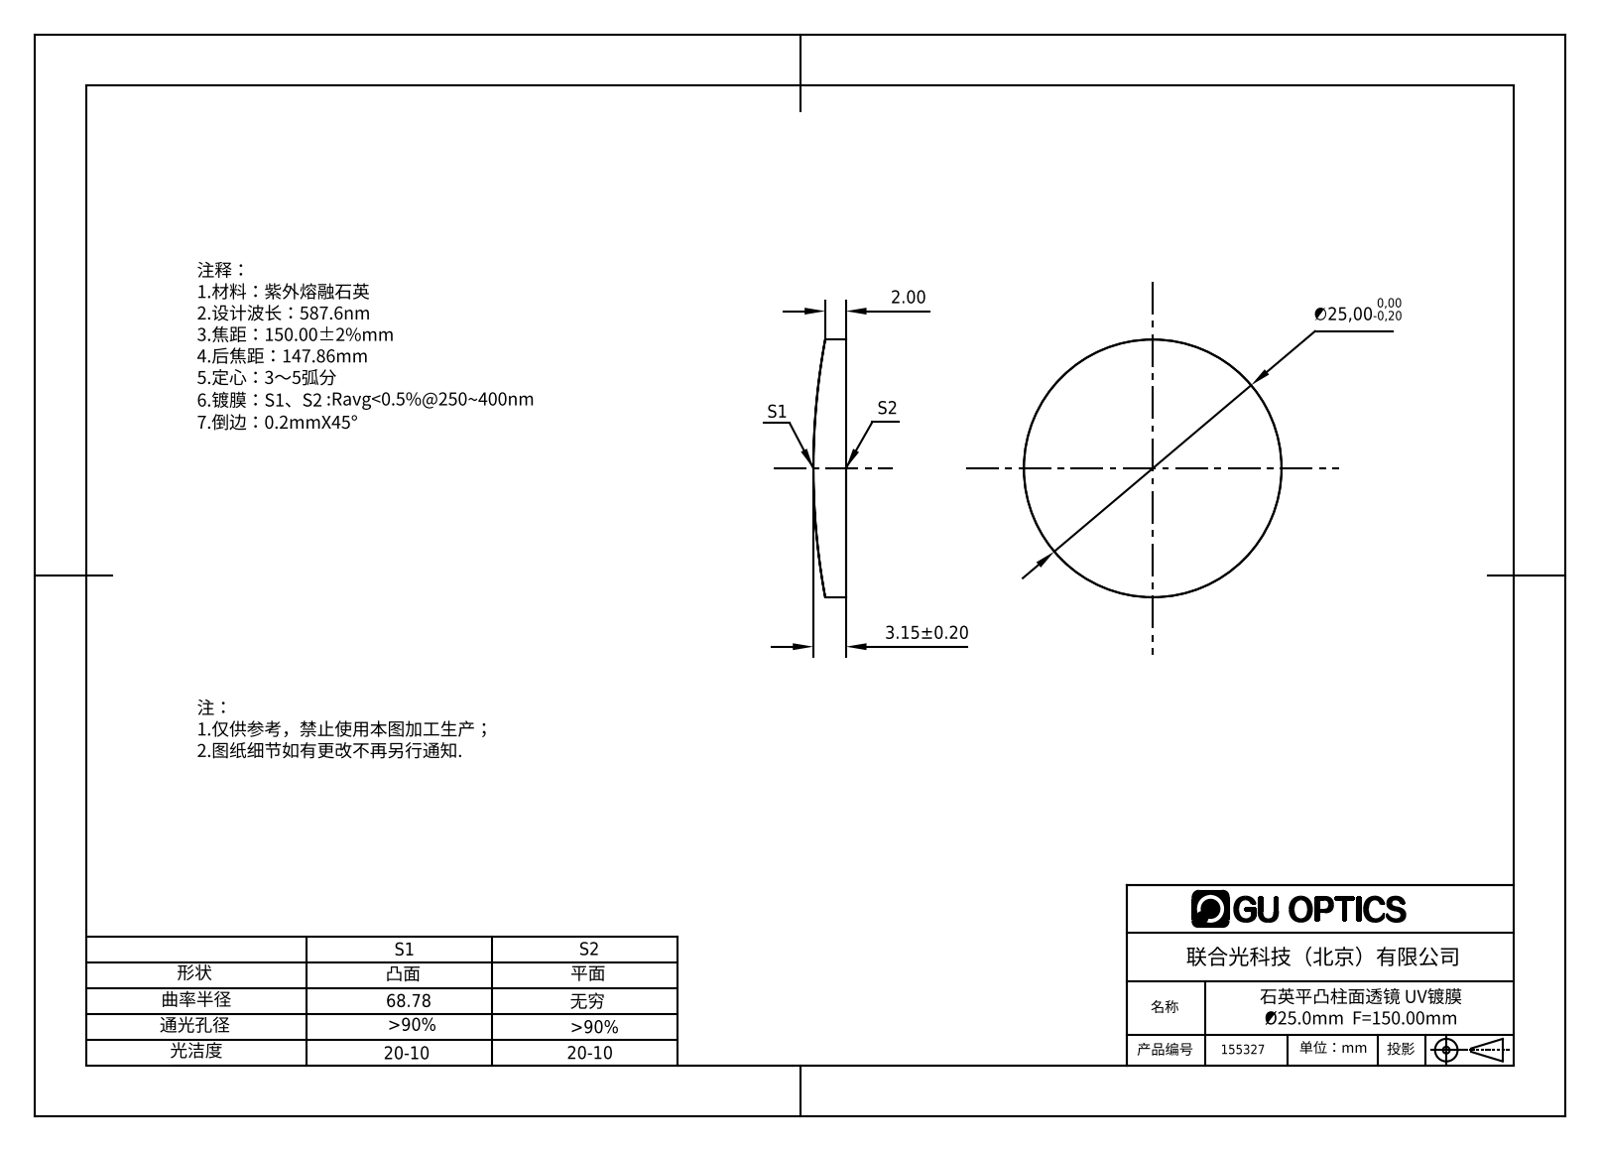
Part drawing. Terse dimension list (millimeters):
name: 155293
written by: SolidWorks 2016 (AUTOMOTIVE_DESIGN)
unit: mm
bodies: 1 solid, 4 faces (1 planar, 3 cylindrical, 0 other)
size: 25 × 25 × 3.15
volume: 1 406 mm³; area: 1 186 mm²
bosses: 1× ⌀25
rounds: 1× R68.78
